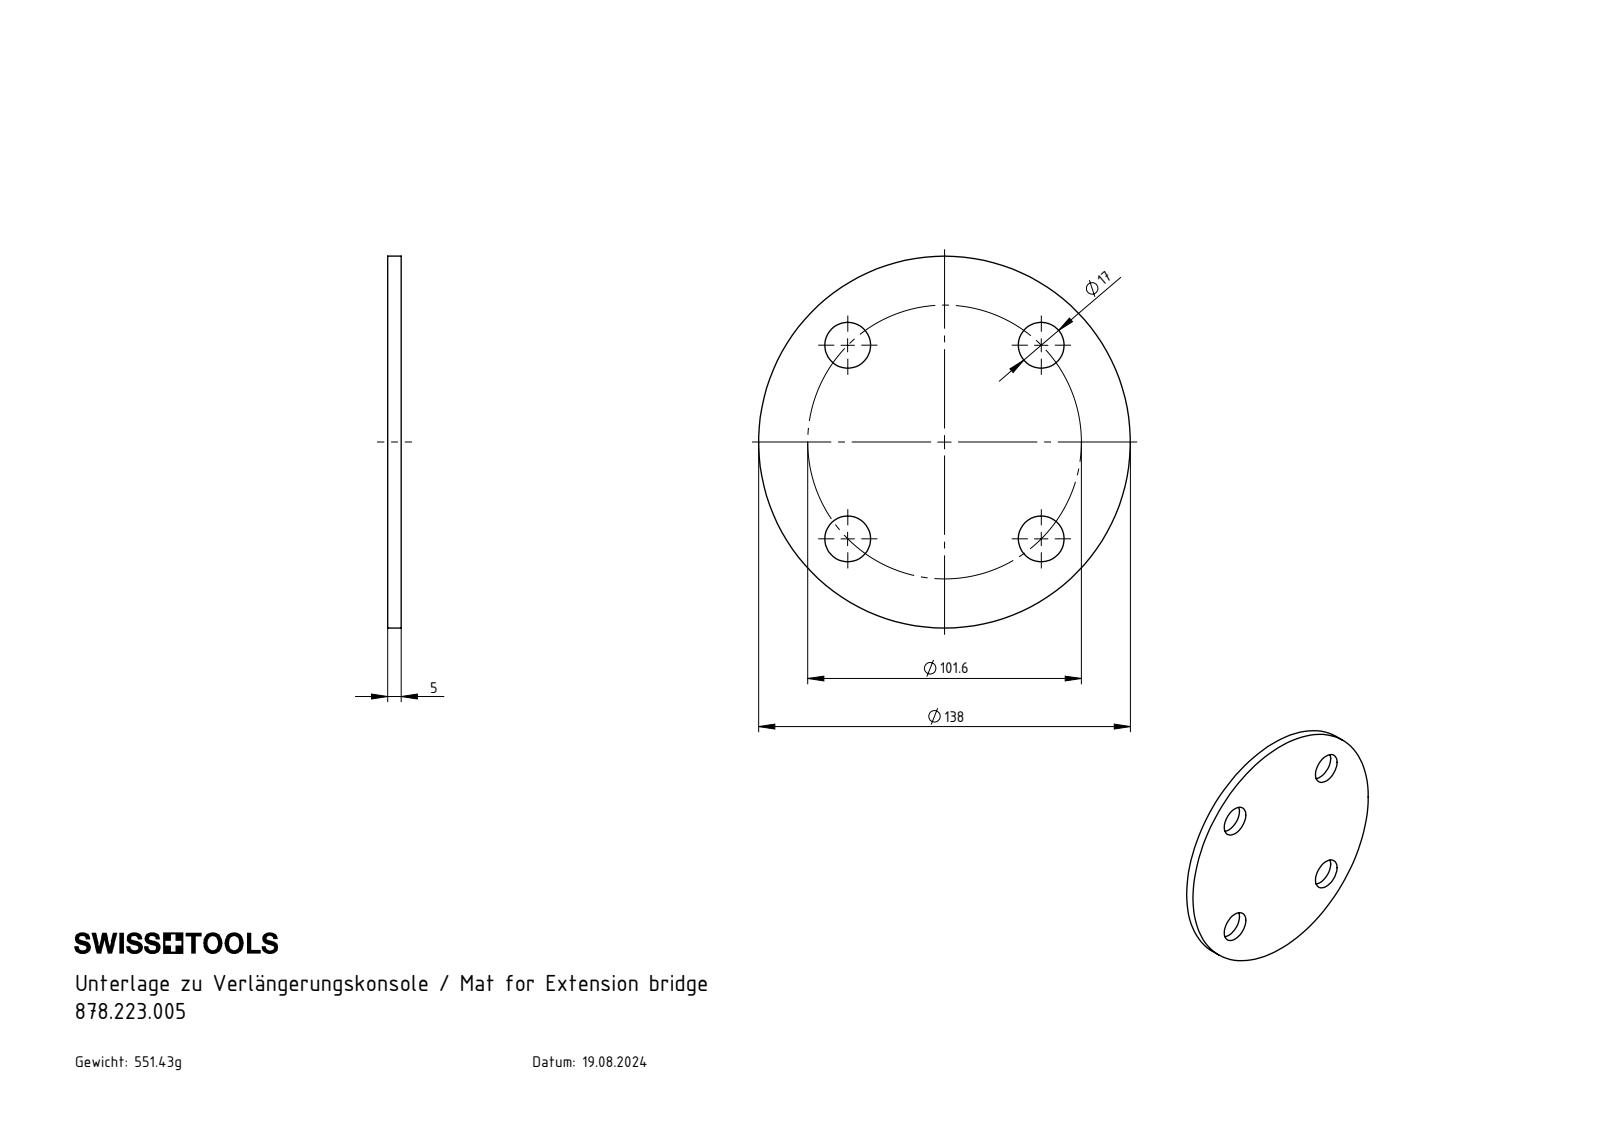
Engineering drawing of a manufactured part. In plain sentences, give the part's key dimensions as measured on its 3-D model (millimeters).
The part is named "878.223.005". Its 3-D file was written by "SolidWorks 2022 (CONFIG_CONTROL_DESIGN)". It is 1 solid with 12 faces: 2 planar, 10 cylindrical and 0 other. Overall it measures 138 by 138 by 5 millimeters. Its volume is 70 246 cubic millimeters and its surface area 31 334 square millimeters. Round holes: 4 of diameter 17. Round bosses or shafts: 1 of diameter 138. The main face-to-face distances are 5. The hole center spacings are 71.84, 101.6.
